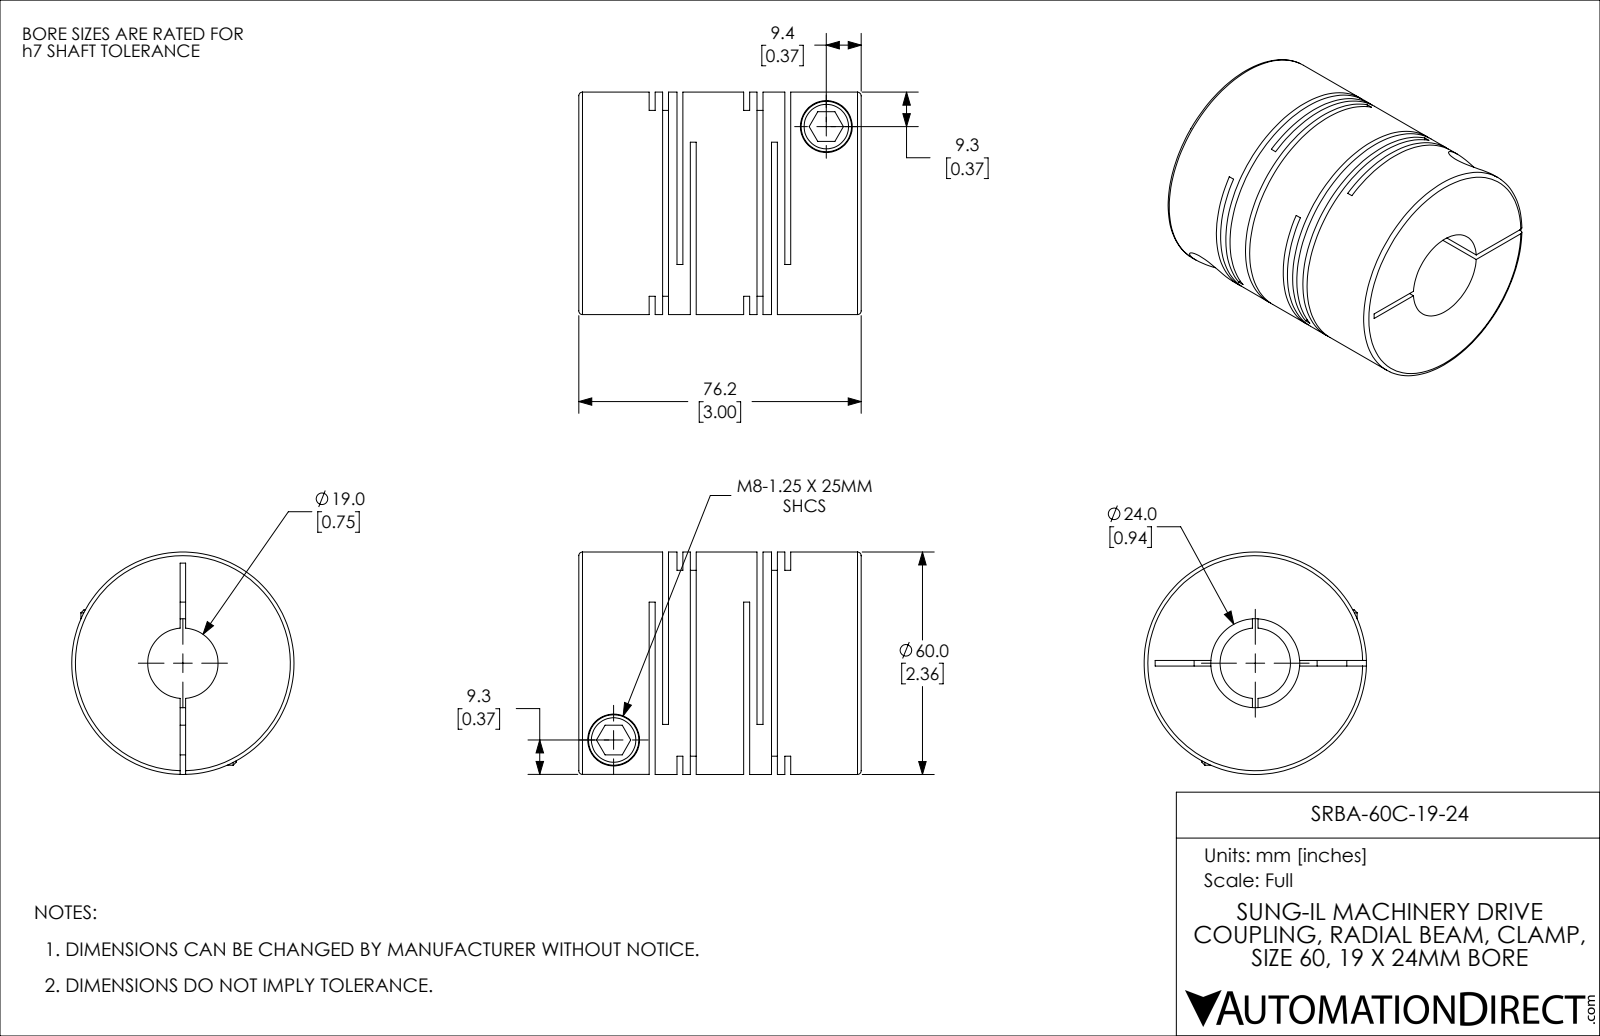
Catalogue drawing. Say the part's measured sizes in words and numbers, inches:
The part is named "SRBA-60C-19-24". Its 3-D file was written by "SolidWorks 2021 (CONFIG_CONTROL_DESIGN)". It is 1 solid with 115 faces: 60 planar, 42 cylindrical and 13 other. Overall it measures 3 by 2.362 by 2.362 inches. Its volume is 9.447 cubic inches and its surface area 88.92 square inches. Round holes: 2 of diameter 0.315, 2 of diameter 0.551, 1 of diameter 0.748, 1 of diameter 0.945. Round bosses or shafts: 2 of diameter 0.535, 1 of diameter 2.362. The main face-to-face distances are 0.063, 0.142, 0.295, 1.004, 1.299, 1.067, 0.232, 0.941, 0.709, 0.079.
